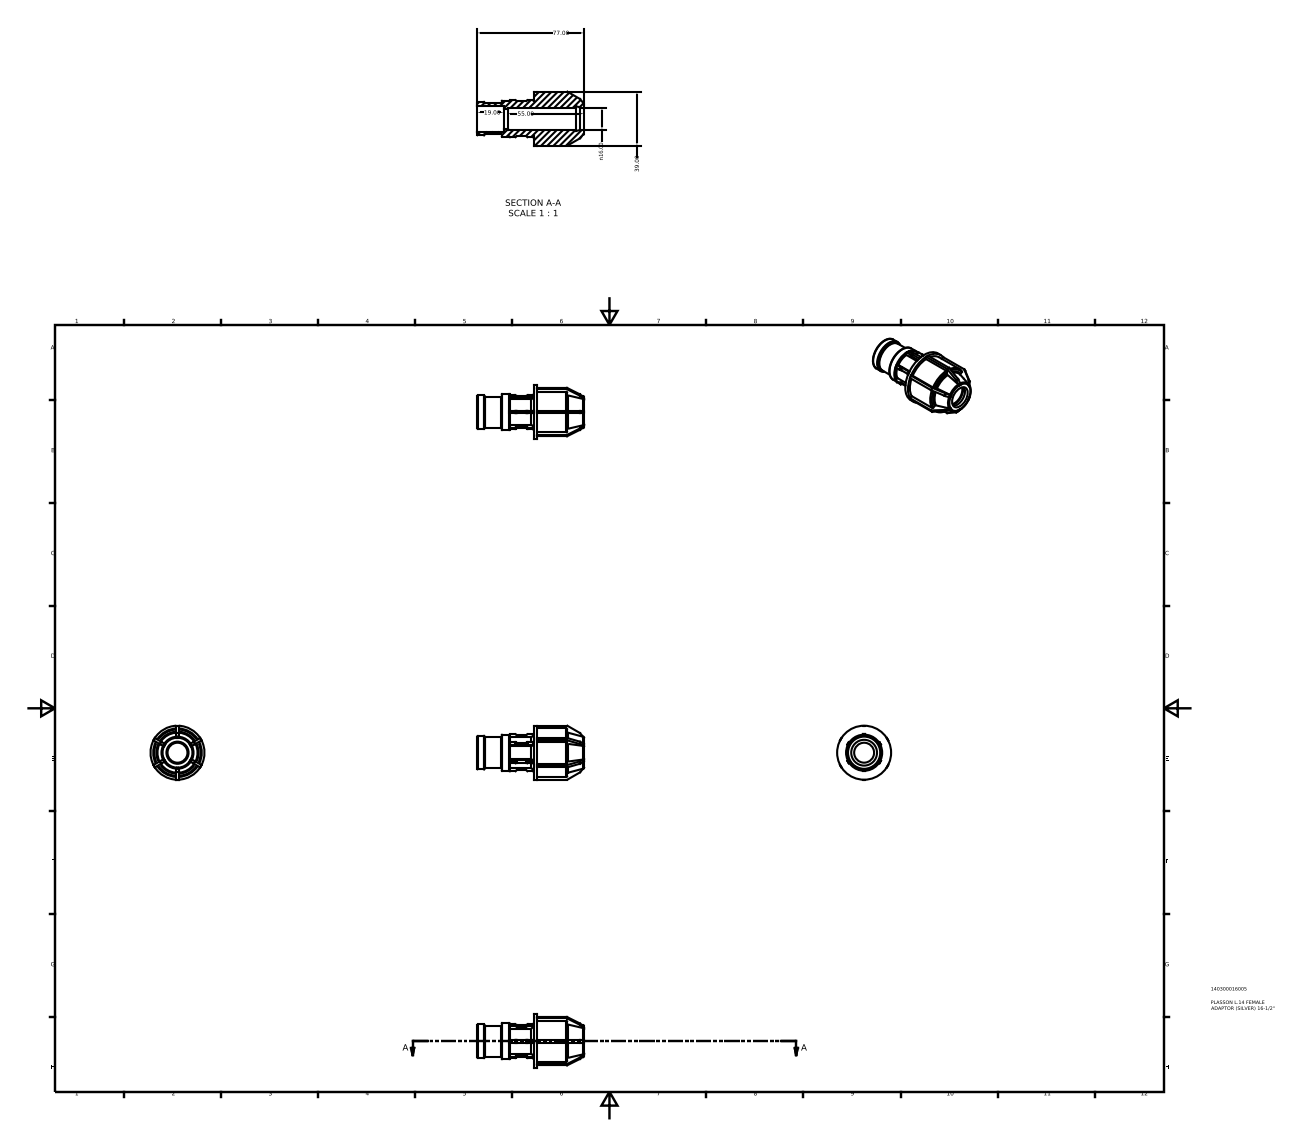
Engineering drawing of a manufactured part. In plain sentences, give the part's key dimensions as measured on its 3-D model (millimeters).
The part is named "140300016005". Its 3-D file was written by "Autodesk Inventor 2015 (AUTOMOTIVE_DESIGN)". It is 1 solid with 255 faces: 159 planar, 68 cylindrical and 28 other. Overall it measures 77 by 39 by 39 millimeters. Its volume is 32 254 cubic millimeters and its surface area 14 024 square millimeters. Round holes: 1 of diameter 14.4, 1 of diameter 16, 1 of diameter 18.63. Round bosses or shafts: 1 of diameter 39, 1 of diameter 35.1, 1 of diameter 26.08, 1 of diameter 24.22, 1 of diameter 22.36. Partial cylindrical surfaces (rounded edges, fillets, slot ends): 48 of radius 0.48. The main face-to-face distances are 1.95, 1.94, 2.75, 1.96, 33.55, 36.3, 40.7, 43.45, 77, 4.35.
